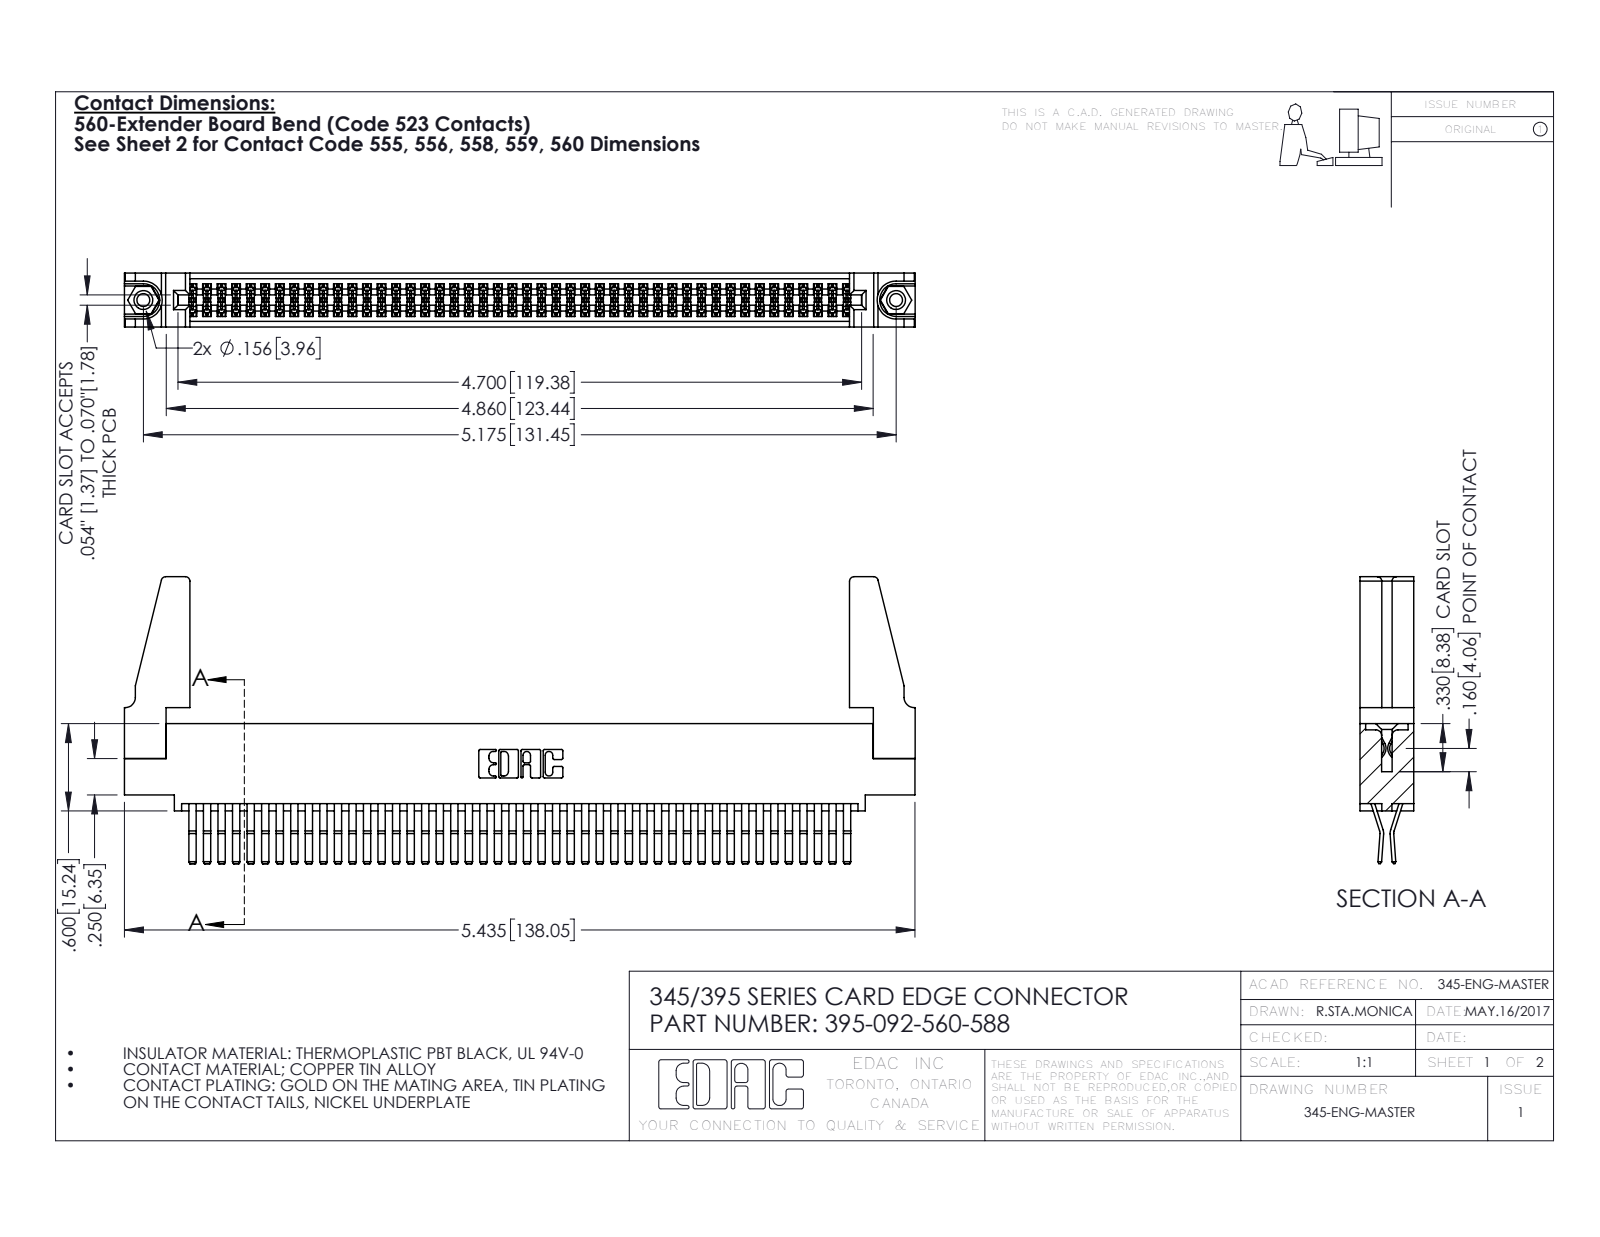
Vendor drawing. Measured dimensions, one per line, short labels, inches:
name: 345-250-001_345-250-001-102; 345 Part_0.110 Offset - 0.156 Dia-TH; 345-292-001_560 Tail; 395-092-560-588 (+1 more)
written by: SolidWorks 2016 (CONFIG_CONTROL_DESIGN)
unit: in
bodies: 97 solids, 5038 faces (3192 planar, 1830 cylindrical, 16 other)
size: 5.436 × 1.972 × 0.37
volume: 1.052 in³; area: 39.54 in²
holes: 2× ⌀0.089, 2× ⌀0.125, 2× ⌀0.156, 1× ⌀0.064
bosses: 2× ⌀0.155
rounds: 138× R0.006, 22× R0.01, 8× R0.03, 6× R0.007, 6× R0.031, 3× R0.026, 2× R0.01, 2× R0.014
face distances: 0.072, 0.298, 0.025, 0.37, 0.2, 0.098, 0.272, 0.225, 0.175, 0.149
hole spacings: 0.27, 4.939, 5.175
